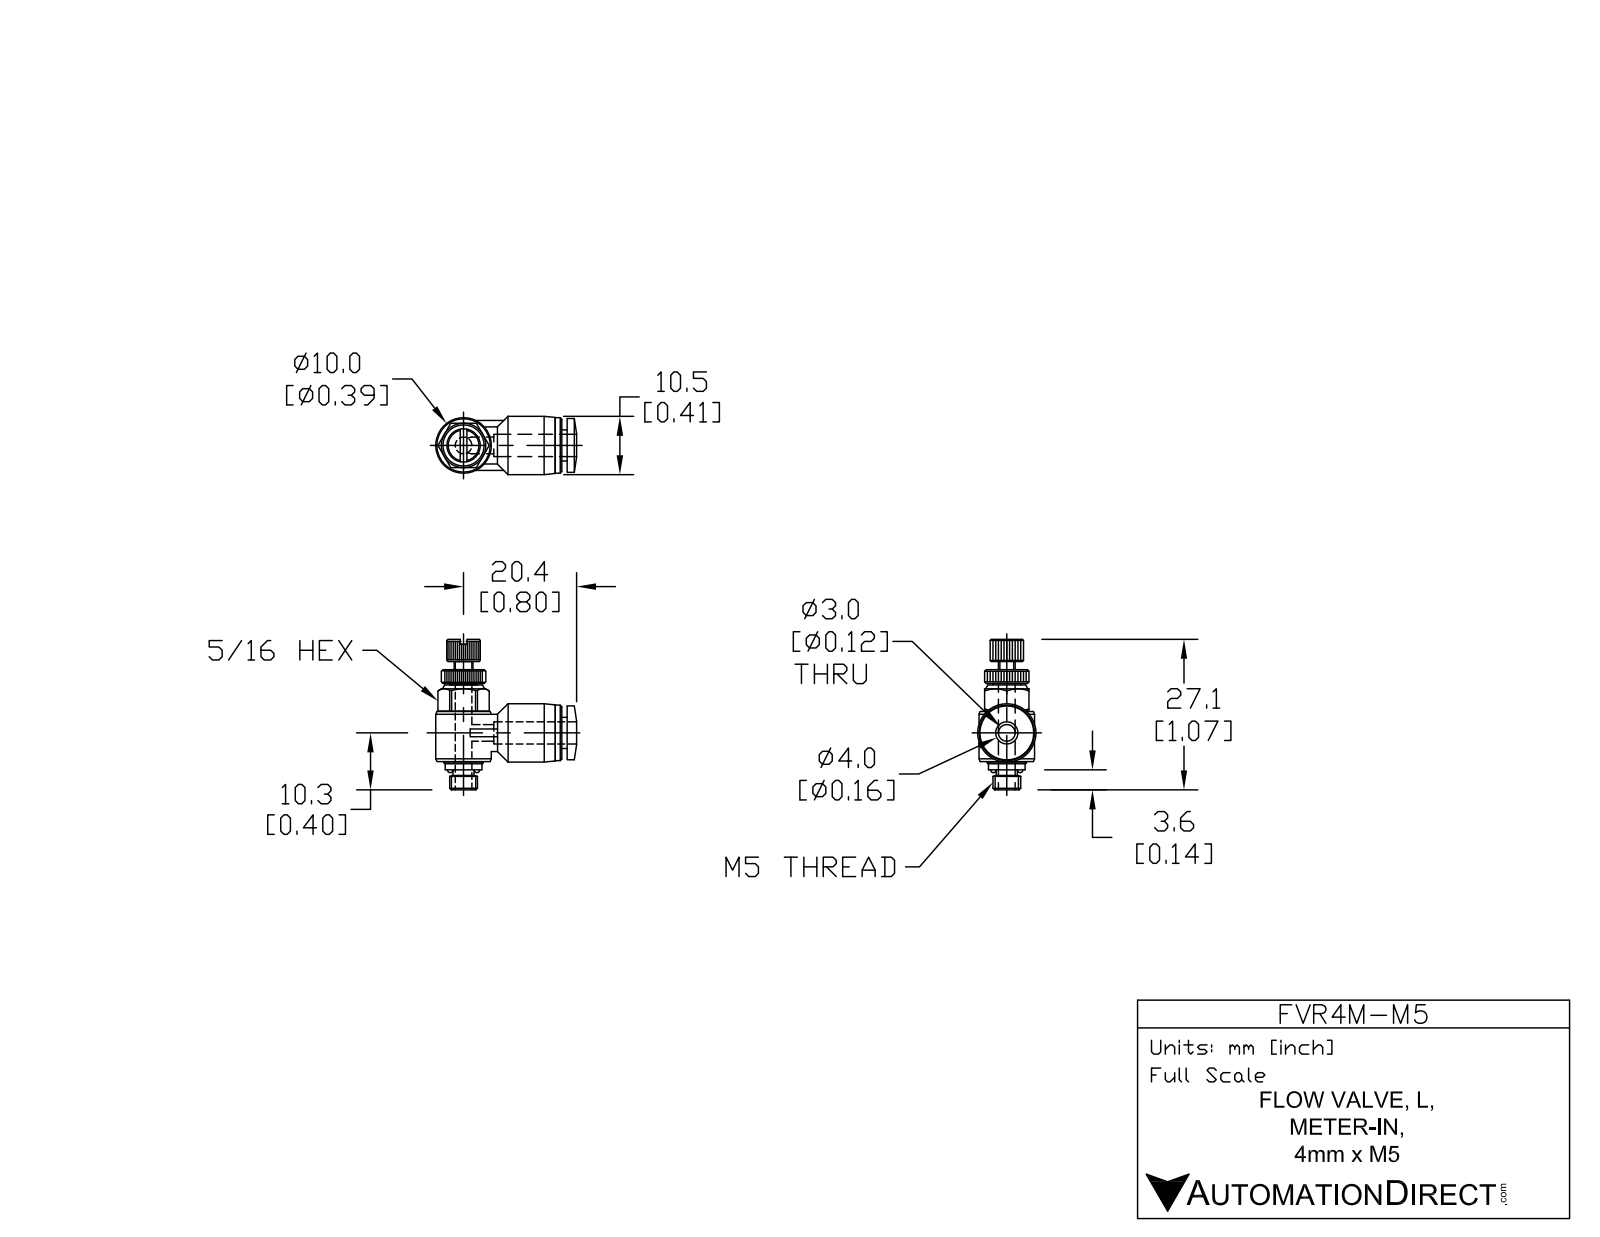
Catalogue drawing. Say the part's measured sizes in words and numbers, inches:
The part is named "FVR4M-M5". Its 3-D file was written by "SolidWorks 2015 (AUTOMOTIVE_DESIGN)". It is 2 solids with 341 faces: 150 planar, 96 cylindrical and 95 other. Overall it measures 1.146 by 0.998 by 0.413 inches. Its volume is 0.136 cubic inches and its surface area 3.003 square inches. Round holes: 2 of diameter 0.059, 1 of diameter 0.15, 1 of diameter 0.169. Round bosses or shafts: 2 of diameter 0.394, 1 of diameter 0.413, 1 of diameter 0.382, 1 of diameter 0.299, 1 of diameter 0.28, 1 of diameter 0.265, 1 of diameter 0.264, 1 of diameter 0.26. Partial cylindrical surfaces (rounded edges, fillets, slot ends): 1 of radius 0.118, 1 of radius 0.157. The main face-to-face distances are 0.315, 0.037, 0.652, 0.354, 0.157, 0.206, 0.293, 0.297, 0.402, 0.156.
